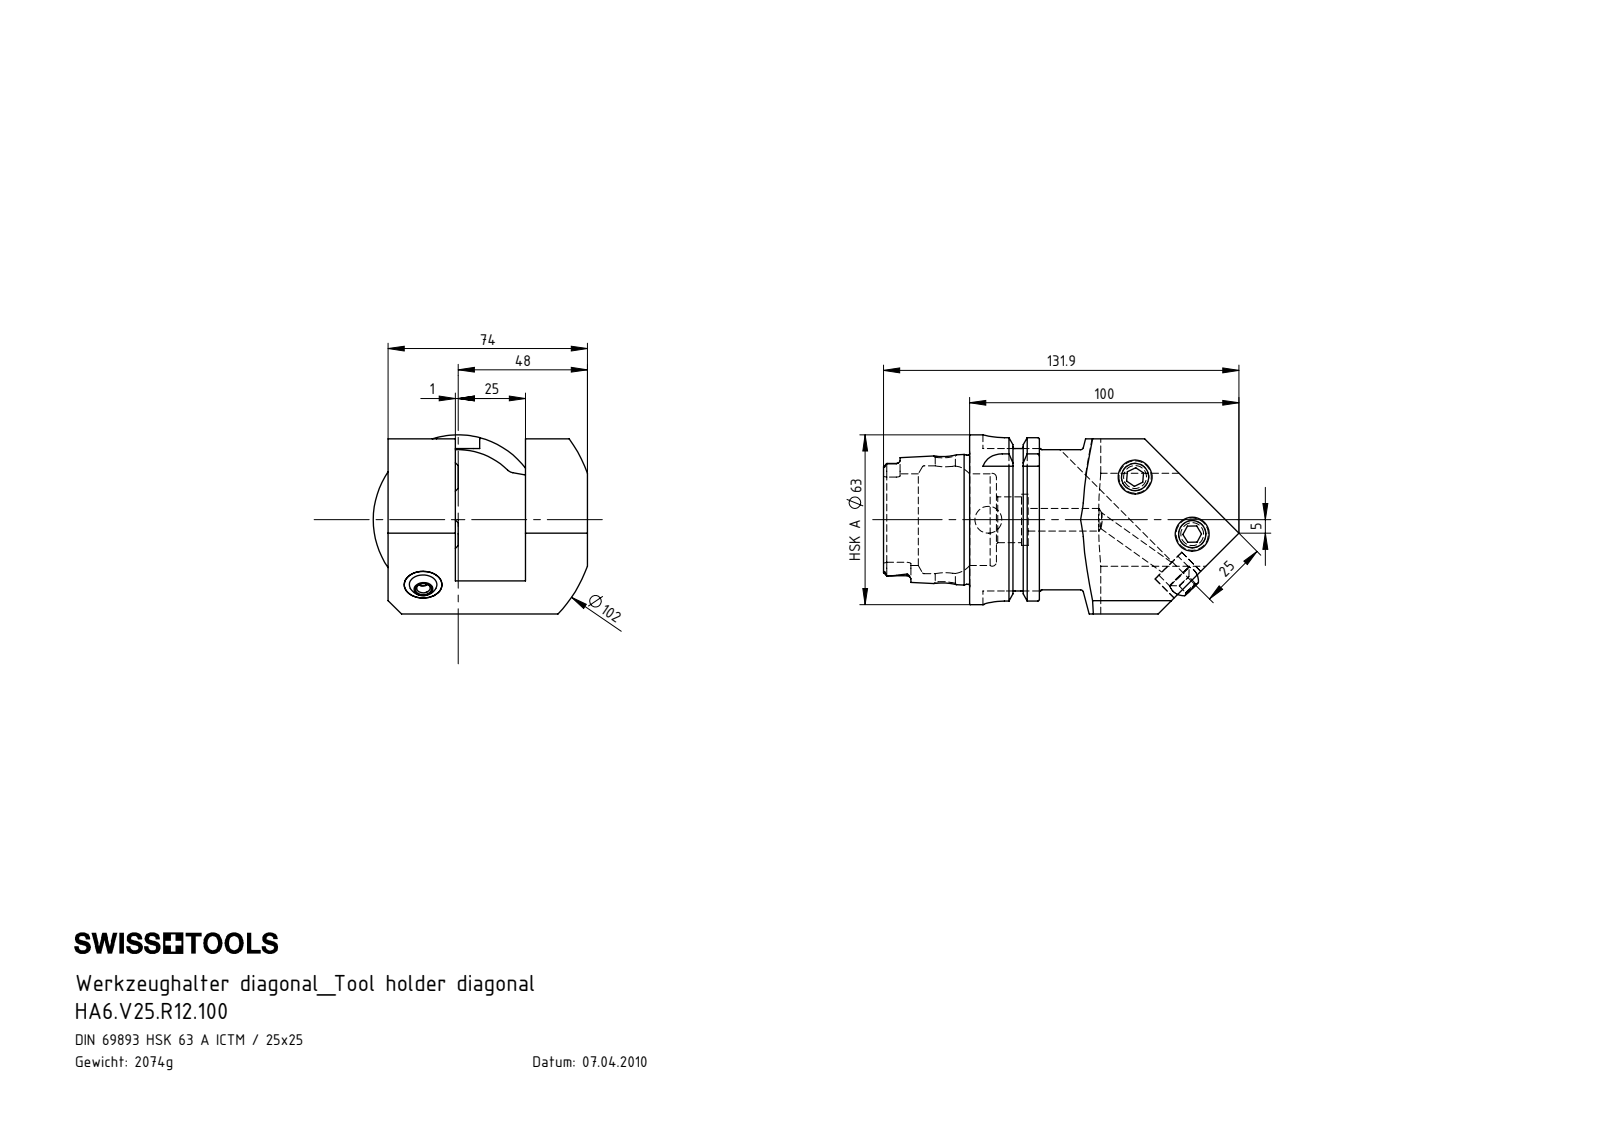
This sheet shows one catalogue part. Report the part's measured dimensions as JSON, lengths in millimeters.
{"part_name": "KU1-U14.001.012_2; HA6-V25.R12.100_C; HA6.V25.R12.100; ISO 4026 - M12 x 25 (+2 more)", "step_written_by": "SolidWorks 2017 (AUTOMOTIVE_DESIGN)", "units": "millimeters", "bodies": {"solids": 5, "faces": 236, "planar": 80, "cylindrical": 65, "other": 91}, "overall_size": [131.9, 79.5, 66.5], "volume_mm3": 264809, "surface_area_mm2": 48164, "round_holes": [[5, 2], [10, 2], [10.2, 2], [7.5, 1], [8.4, 1], [14, 1], [17, 1], [19, 1], [34, 1], [40, 1]], "round_bosses_or_shafts": [[12, 2], [63, 1], [54.95, 1], [52, 1], [47.94, 1], [14, 1]], "partial_cylinders_radius": [[1.4, 6], [8, 4], [2.82, 2], [2.88, 2], [51, 1]], "face_to_face_distances": [25, 74, 23, 51, 26, 49, 65, 16, 25.95, 9.95], "hole_center_spacings": [30, 56.72, 75.87]}
